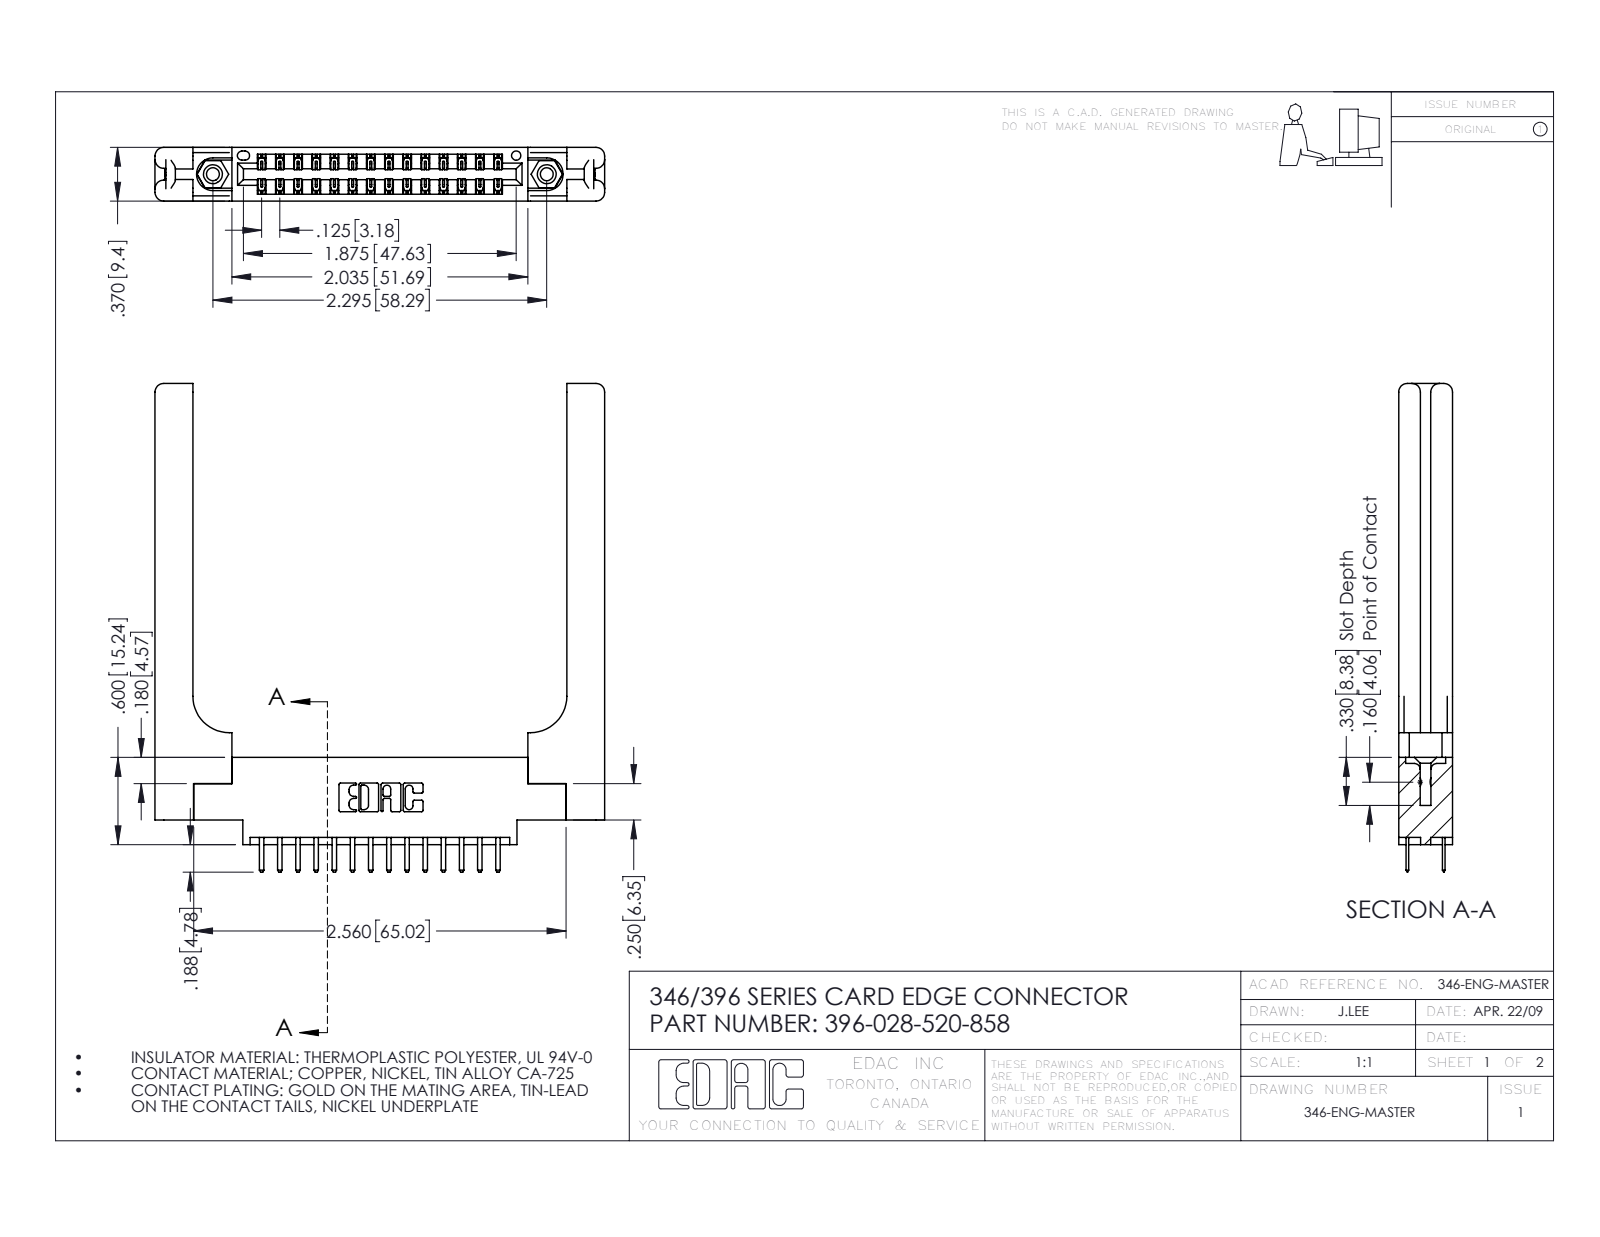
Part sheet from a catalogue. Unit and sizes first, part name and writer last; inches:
Units: inches
Overall size (bounding box): 3.358 × 3.091 × 0.37
Round holes (diameter × count): ⌀0.089 ×2, ⌀0.125 ×2, ⌀0.156 ×2, ⌀0.064 ×1
Round bosses / shafts (diameter × count): ⌀0.155 ×2
Partial cylindrical surfaces — rounded edges, fillets, slot ends (radius × count): R0.006 ×42, R0.01 ×32, R0.01 ×22, R0.06 ×16, R0.007 ×6, R0.031 ×6, R0.026 ×3, R0.014 ×2
Main face-to-face distances: 0.37, 0.15, 0.072, 0.148, 0.048, 0.322, 0.25, 0.102, 0.22, 0.173
Hole centre spacings: 0.246, 2.089, 2.295
Volume: 0.901 in³ · Surface area: 22.75 in²
Bodies: 33 solids, 1950 faces (1264 planar, 626 cylindrical, 60 other)
Part name (STEP PRODUCT): 346 Part_0.170 Offset - 0.156 Dia-TH; 346-220-058_345-220-058; 345-292-001_345-293-120; 345-250-001_345-250-001-102 (+1 more)
STEP written by: SolidWorks 2016 (CONFIG_CONTROL_DESIGN)
